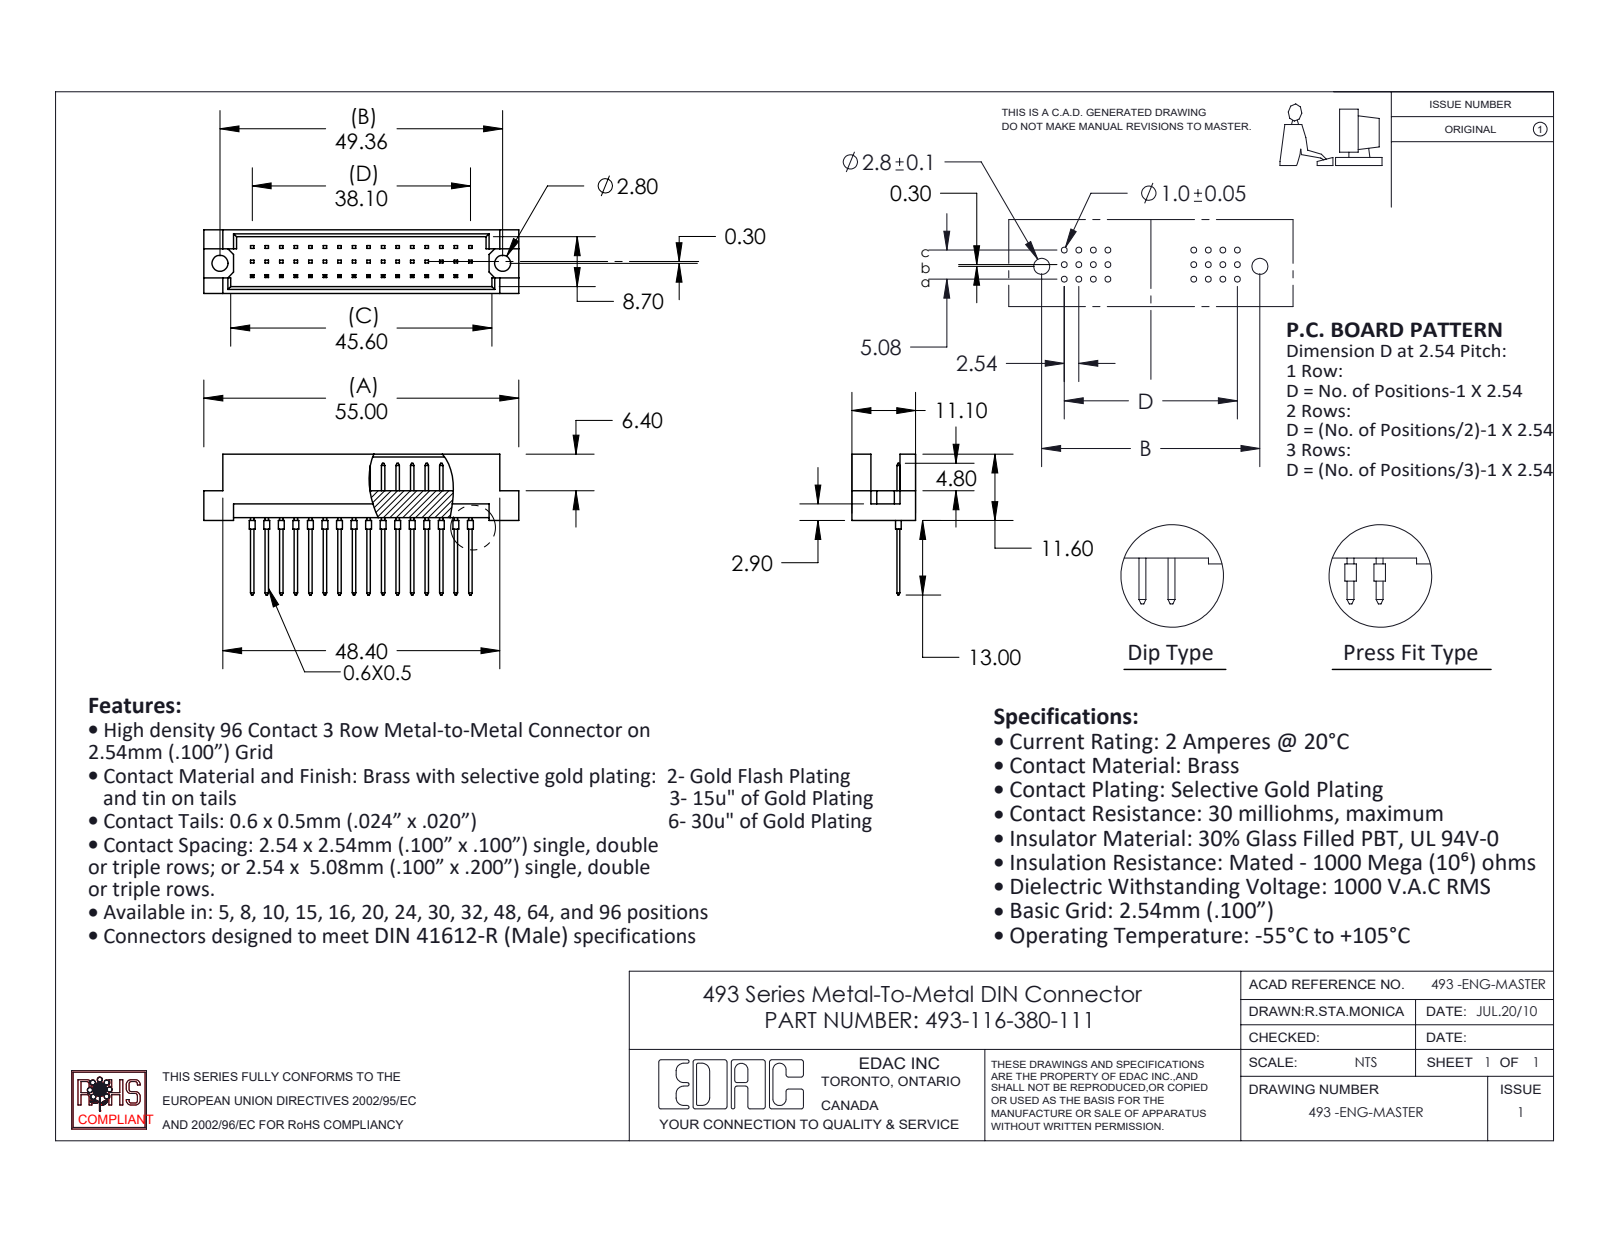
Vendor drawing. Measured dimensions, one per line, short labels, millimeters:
name: 493-290_80; 493-116-380-111; 493 Part_48
written by: SolidWorks 2020 (CONFIG_CONTROL_DESIGN)
unit: mm
bodies: 17 solids, 596 faces (560 planar, 36 cylindrical, 0 other)
size: 55 × 24.6 × 11.1
volume: 3 393 mm³; area: 4 598 mm²
holes: 2× ⌀2.8
bosses: 16× ⌀1
face distances: 1.2, 9.9, 11.1, 0.5, 8.7, 2.54, 4.7, 5.08, 2.76, 8.34
hole spacings: 49.36
